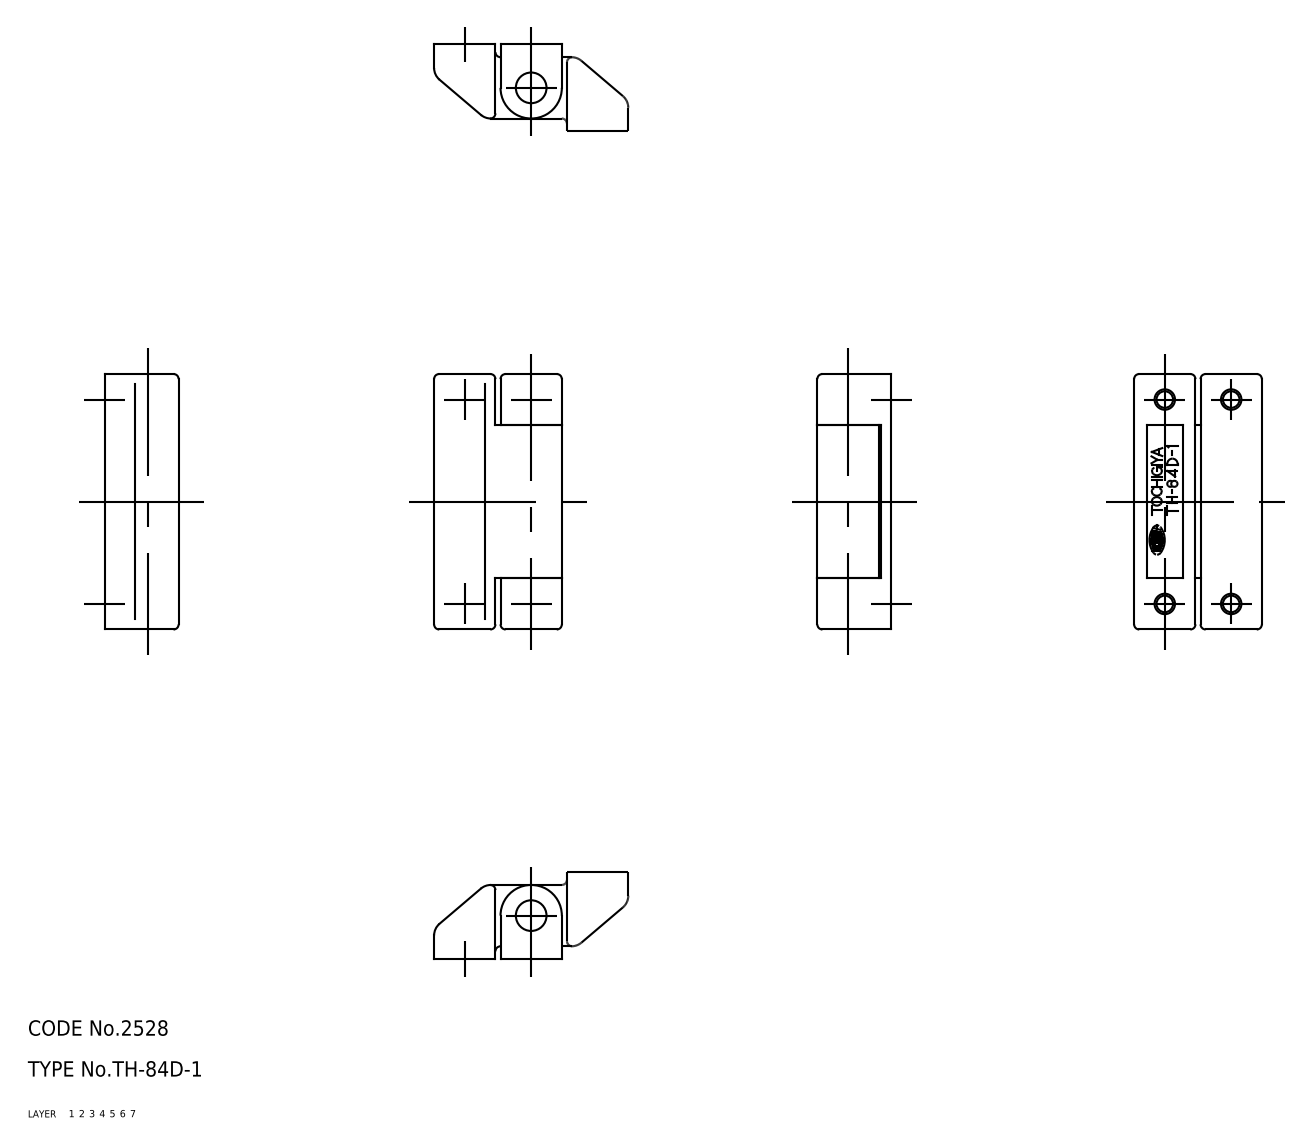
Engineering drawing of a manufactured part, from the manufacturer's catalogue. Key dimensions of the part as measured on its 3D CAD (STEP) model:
Part name (STEP PRODUCT): shaft; hinge piece_B; hinge piece_A; TH_84D_1_18029_36
STEP written by: CADfix (AUTOMOTIVE_DESIGN)
Units: millimetres
Bodies: 3 solids, 78 faces (0 planar, 0 cylindrical, 78 other)
Overall size (bounding box): 50 × 25 × 14.5
Volume: 14 329 mm³ · Surface area: 7 867 mm²
